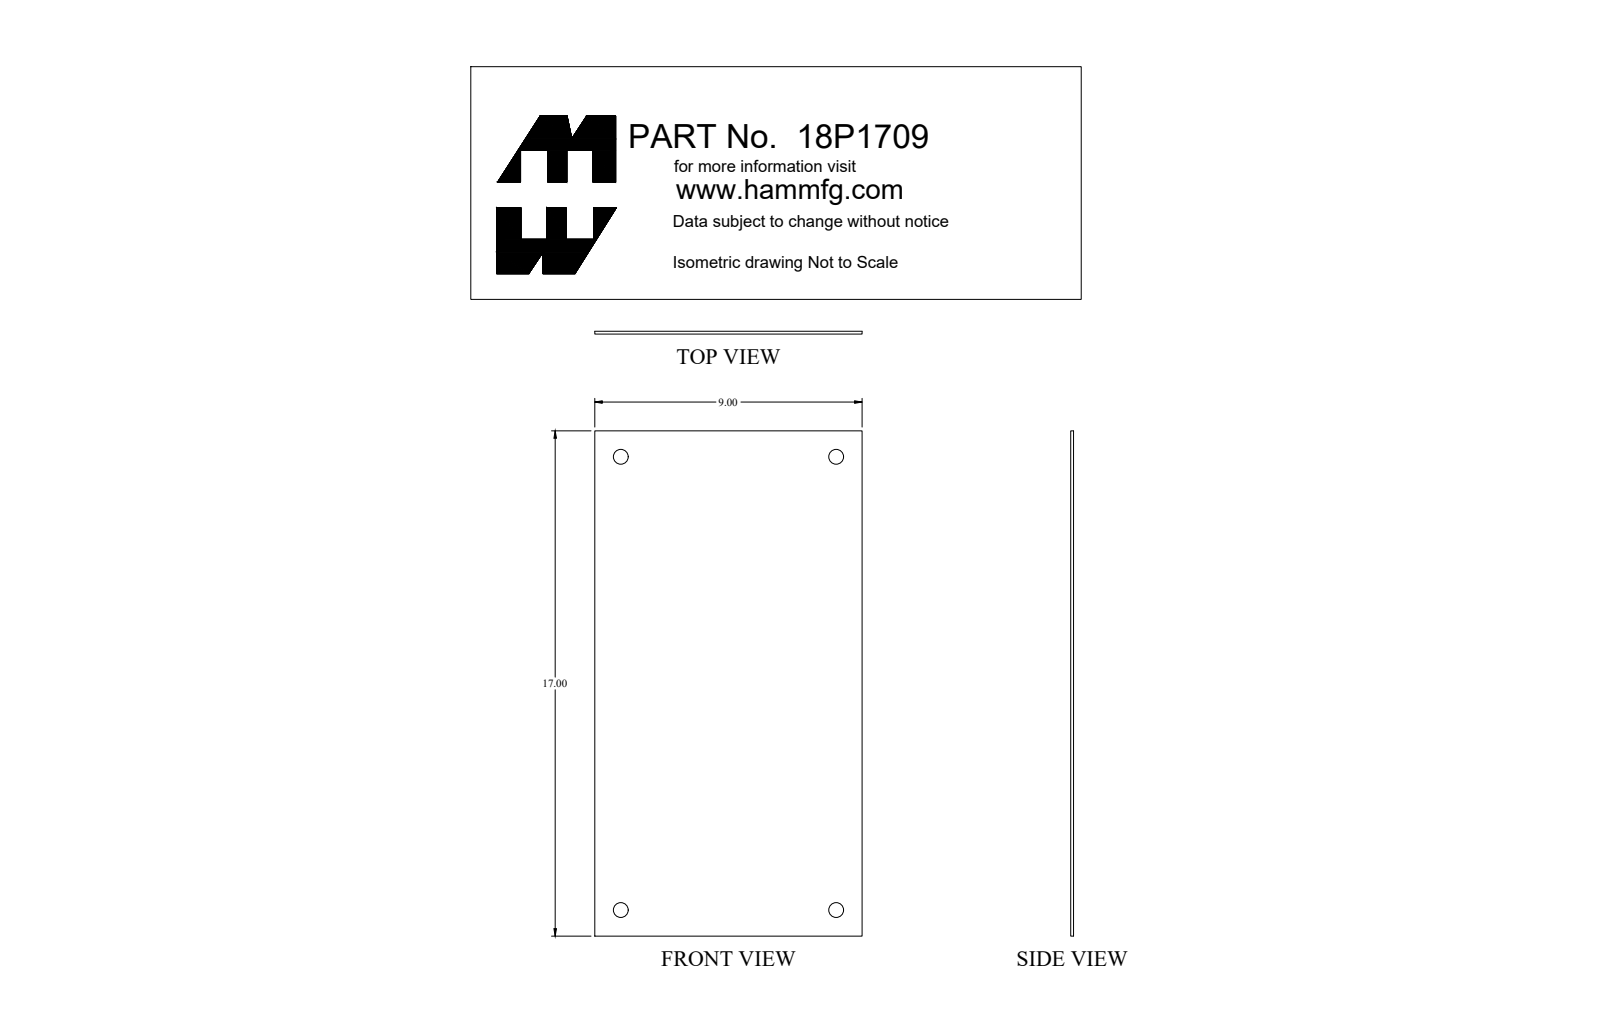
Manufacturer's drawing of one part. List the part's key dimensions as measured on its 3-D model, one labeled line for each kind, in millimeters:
Part name (STEP PRODUCT): 18P1709_Default
STEP written by: SolidWorks 2018 (CONFIG_CONTROL_DESIGN)
Units: millimetres
Bodies: 1 solid, 14 faces (6 planar, 8 cylindrical, 0 other)
Overall size (bounding box): 431.8 × 228.6 × 2.4
Volume: 237 000 mm³ · Surface area: 200 000 mm²
Round holes (diameter × count): ⌀12.7 ×4
Main face-to-face distances: 2.4, 228.6, 431.8
Hole centre spacings: 184.2, 387.4, 428.9
